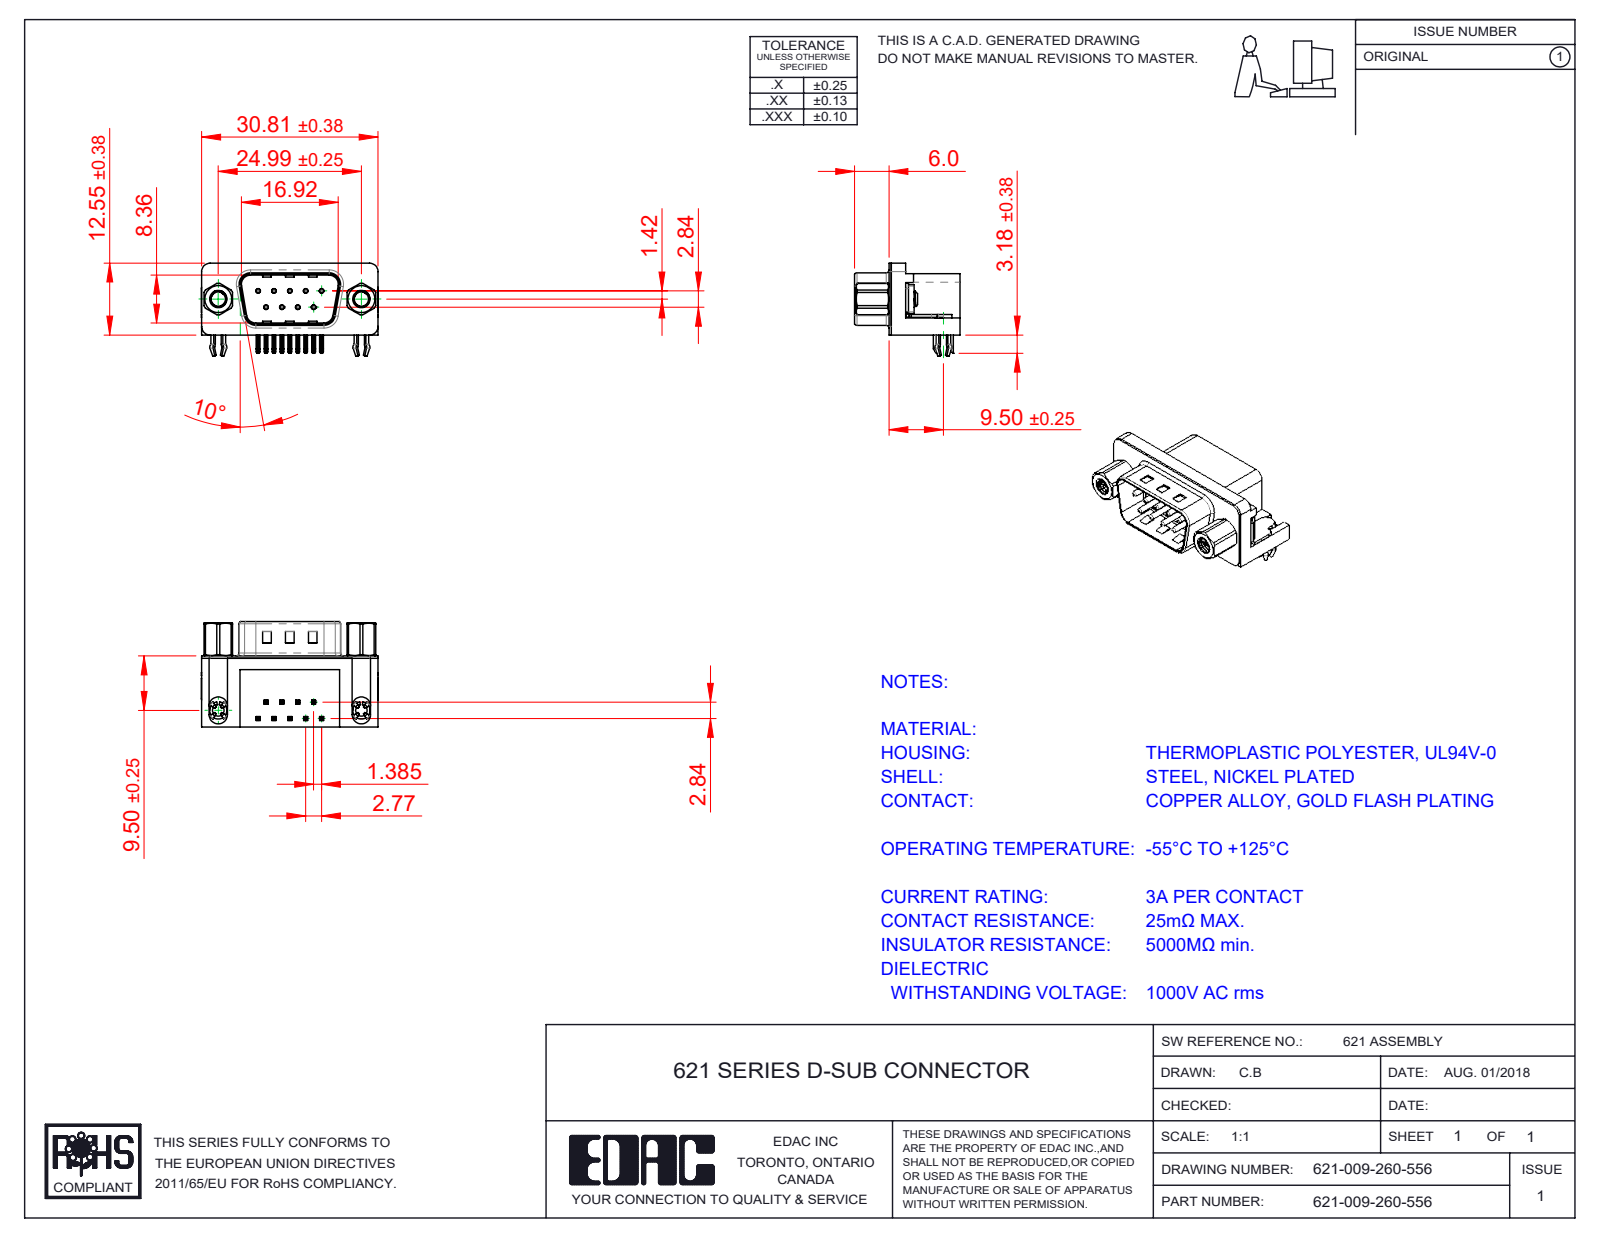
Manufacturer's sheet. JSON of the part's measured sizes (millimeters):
{"part_name": "621 Shell_9 Socket; 621 Housing_9 Socket; 621-009-260-556; 621 M3 Hex Standoff 5 (+4 more)", "step_written_by": "SolidWorks 2016 (CONFIG_CONTROL_DESIGN)", "units": "millimeters", "bodies": {"solids": 17, "faces": 1169, "planar": 595, "cylindrical": 423, "other": 151}, "overall_size": [30.89, 18.4, 15.73], "volume_mm3": 3497, "surface_area_mm2": 5032, "round_holes": [[0.35, 9], [0.8, 9], [2.26, 2], [2.5, 2], [4, 2], [4.8, 2], [5, 2]], "round_bosses_or_shafts": [[0.75, 9], [4.9, 2], [4.75, 2], [3.9, 2], [3.26, 2], [3, 2]], "partial_cylinders_radius": [[0.25, 44], [0.12, 18], [1, 16], [0.5, 9], [1.5, 8], [1.6, 8], [0.9, 4], [2, 4]], "face_to_face_distances": [0.4, 12, 12.4, 10.35, 9.5, 2.5, 2.9, 0.5, 2.1, 0.35], "hole_center_spacings": [3.16, 2.77, 5.54, 5.03, 5.04, 8.31, 7.48, 7.49]}
